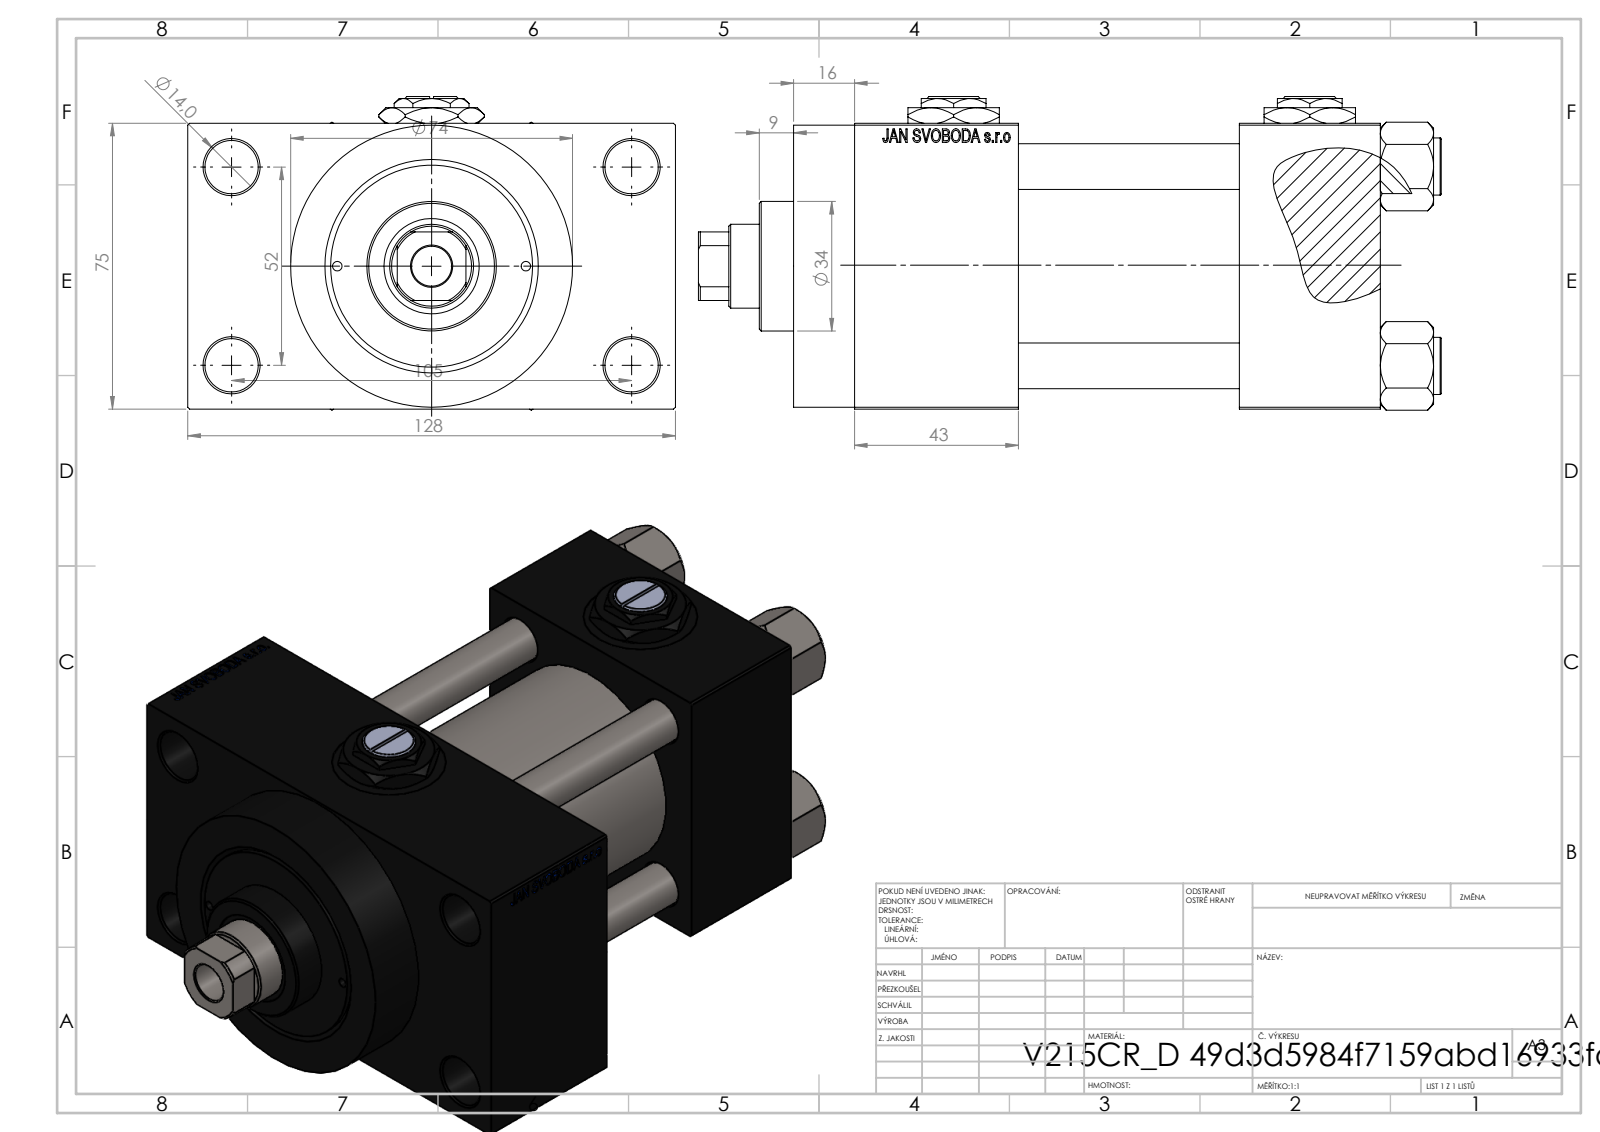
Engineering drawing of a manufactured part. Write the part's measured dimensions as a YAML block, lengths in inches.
part_name: "V215CR_D_Body; NUT_M5_D; V215_VC_A; V215CR_D_TYCINKA (+2 more)"
step_written_by: "SolidWorks 2019 (CONFIG_CONTROL_DESIGN)"
units: inches
bodies: {solids: 13, faces: 1212, planar: 547, cylindrical: 103, other: 562}
overall_size: [7.677, 5.039, 3.239]
volume: 48.39
surface_area: 264.8
round_holes:
  - {diameter: 0.472, count: 4}
  - {diameter: 0.551, count: 4}
  - {diameter: 0.825, count: 4}
  - {diameter: 1.181, count: 4}
  - {diameter: 0.276, count: 3}
  - {diameter: 0.098, count: 2}
  - {diameter: 0.413, count: 1}
  - {diameter: 0.866, count: 1}
  - {diameter: 0.984, count: 1}
  - {diameter: 1.614, count: 1}
  - {diameter: 1.969, count: 1}
  - {diameter: 2.087, count: 1}
round_bosses_or_shafts:
  - {diameter: 0.591, count: 4}
  - {diameter: 2.913, count: 1}
  - {diameter: 2.205, count: 1}
  - {diameter: 1.339, count: 1}
partial_cylinders:
  - {radius: 0.413, count: 1}
face_to_face_distances: [2.953, 2.283, 1.457, 3.74, 1.043, 5.433, 3.976, 1.693, 3.996, 0.63]
hole_center_spacings: [1.031, 1.037, 1.456, 1.497, 2.059, 2.253, 2.3, 2.307]
